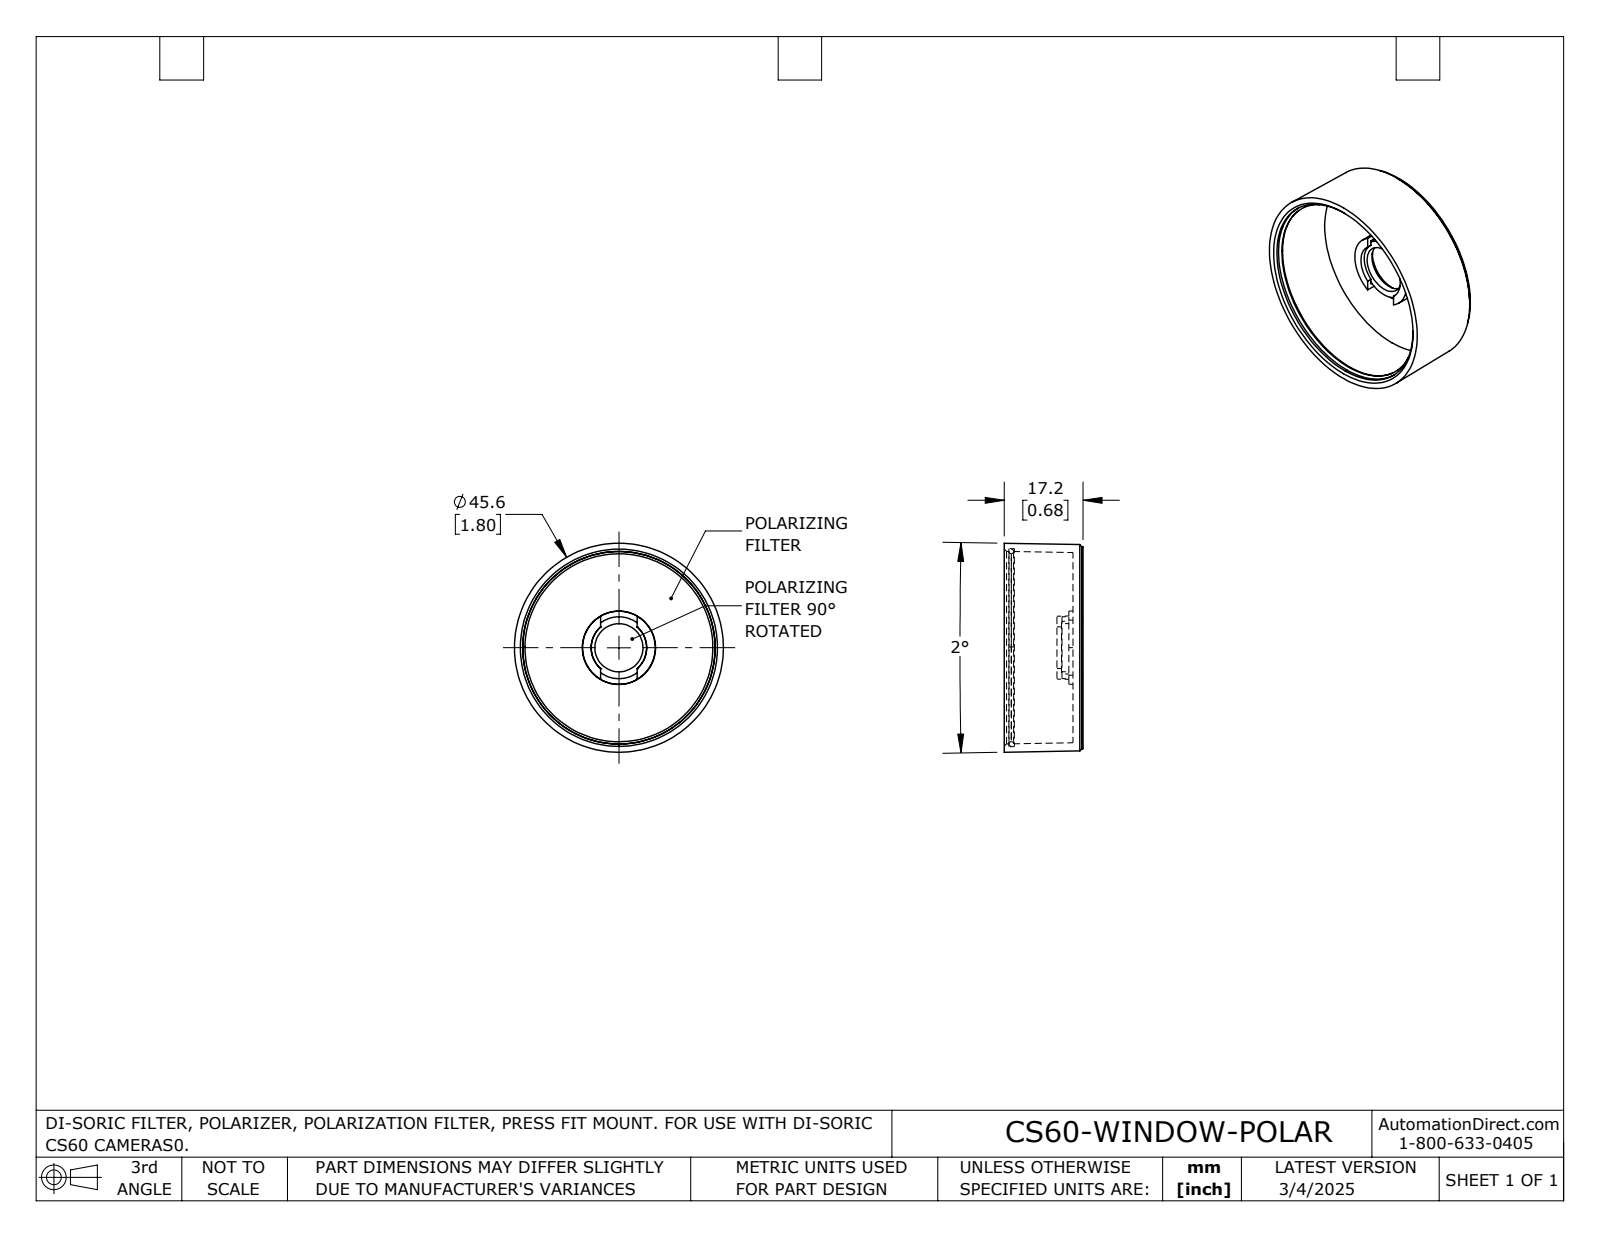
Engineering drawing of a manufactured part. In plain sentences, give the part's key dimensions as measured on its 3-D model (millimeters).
The part is named "CS60-WINDOW-POLAR". Its 3-D file was written by "SolidWorks 2024 (AUTOMOTIVE_DESIGN)". It is 5 solids with 53 faces: 21 planar, 22 cylindrical and 10 other. Overall it measures 45.6 by 45.6 by 17.2 millimeters. Its volume is 7 410 cubic millimeters and its surface area 11 680 square millimeters. Round holes: 1 of diameter 10.5, 1 of diameter 12.5, 1 of diameter 43.2. Round bosses or shafts: 1 of diameter 44, 1 of diameter 13.5, 1 of diameter 12.3. Partial cylindrical surfaces (rounded edges, fillets, slot ends): 4 of radius 0.3, 4 of radius 0.4, 1 of radius 7. The main face-to-face distances are 2, 2.2, 15, 17, 17.2, 14.1, 0.9, 2.9, 3.1, 1.
